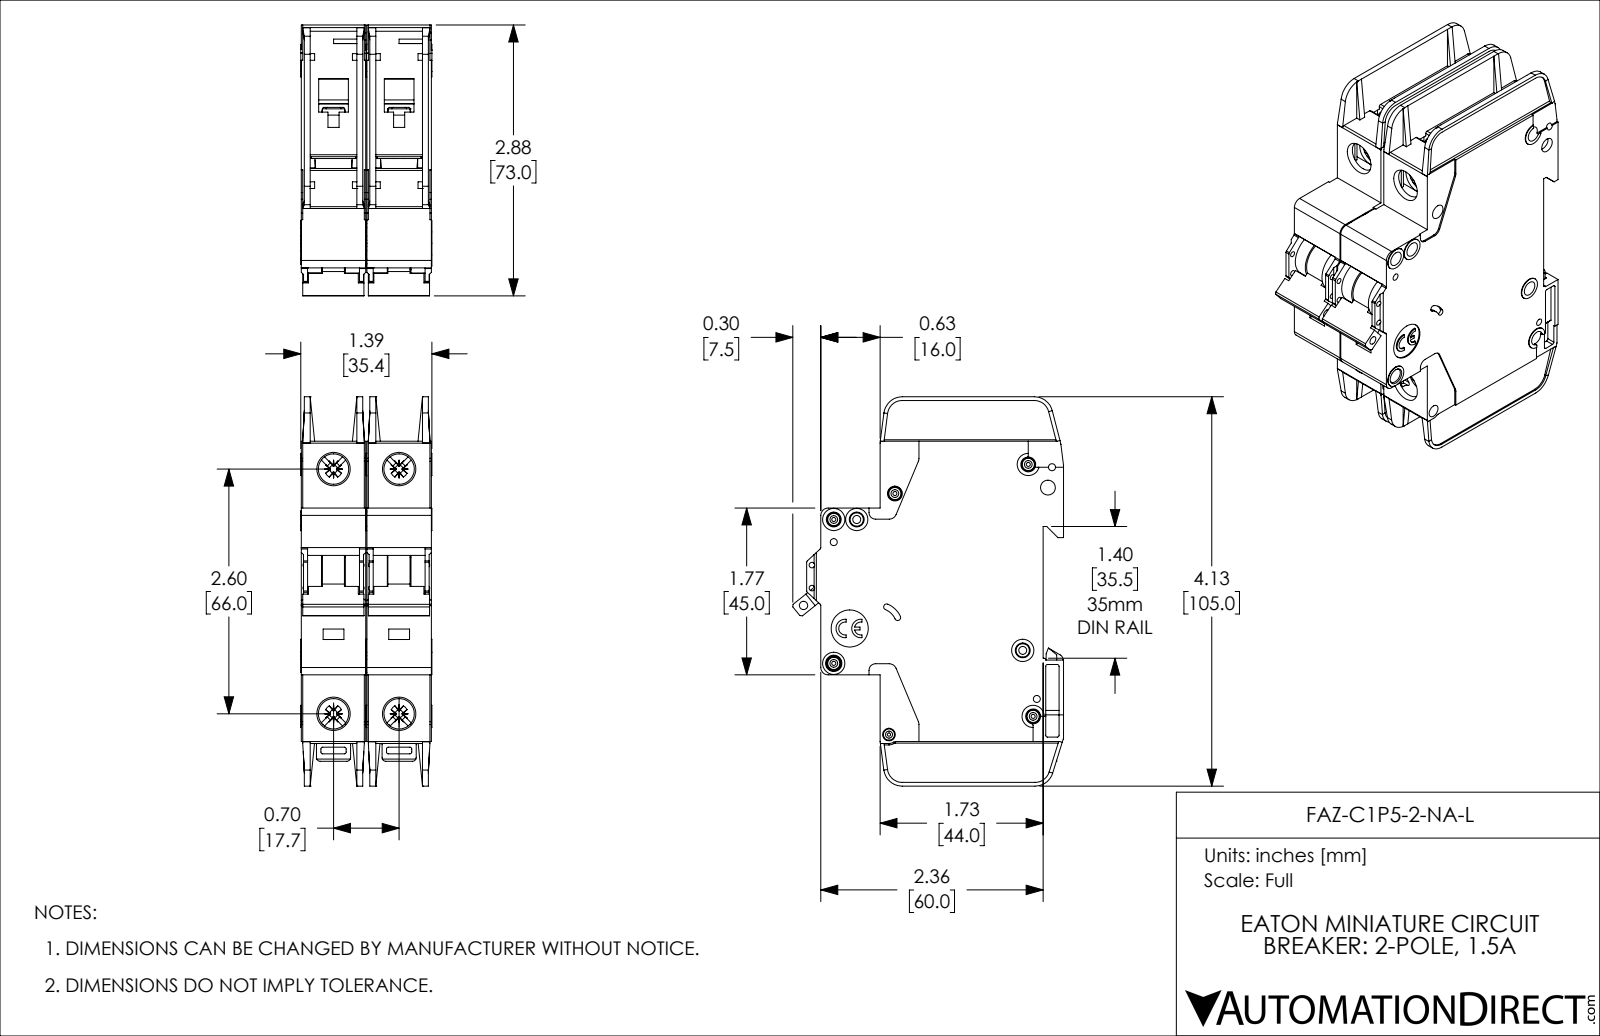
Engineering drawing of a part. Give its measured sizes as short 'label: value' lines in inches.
name: FAZ-C1P5-2-NA-L
written by: SolidWorks 2019 (AUTOMOTIVE_DESIGN)
unit: in
bodies: 2 solids, 2254 faces (1342 planar, 714 cylindrical, 198 other)
size: 4.134 × 2.876 × 1.394
volume: 9.365 in³; area: 82.01 in²
holes: 8× ⌀0.157, 5× ⌀0.043, 4× ⌀0.075, 4× ⌀0.323, 2× ⌀0.059, 2× ⌀0.085, 1× ⌀0.035, 1× ⌀0.089, 1× ⌀0.098, 1× ⌀0.134, 1× ⌀0.394
bosses: 5× ⌀0.13, 4× ⌀0.236, 3× ⌀0.118, 2× ⌀0.098
rounds: 57× R0.02, 20× R0.016, 14× R0.039, 10× R0.079, 8× R0.043, 5× R0.008, 5× R0.197, 4× R0.01
face distances: 0.697, 0.047, 0.685, 0.591, 0.094, 0.638, 0.543, 1.382, 0.744, 0.65
hole spacings: 0.244, 0.537, 0.697, 0.87, 2.598, 2.69, 0.189, 0.199
